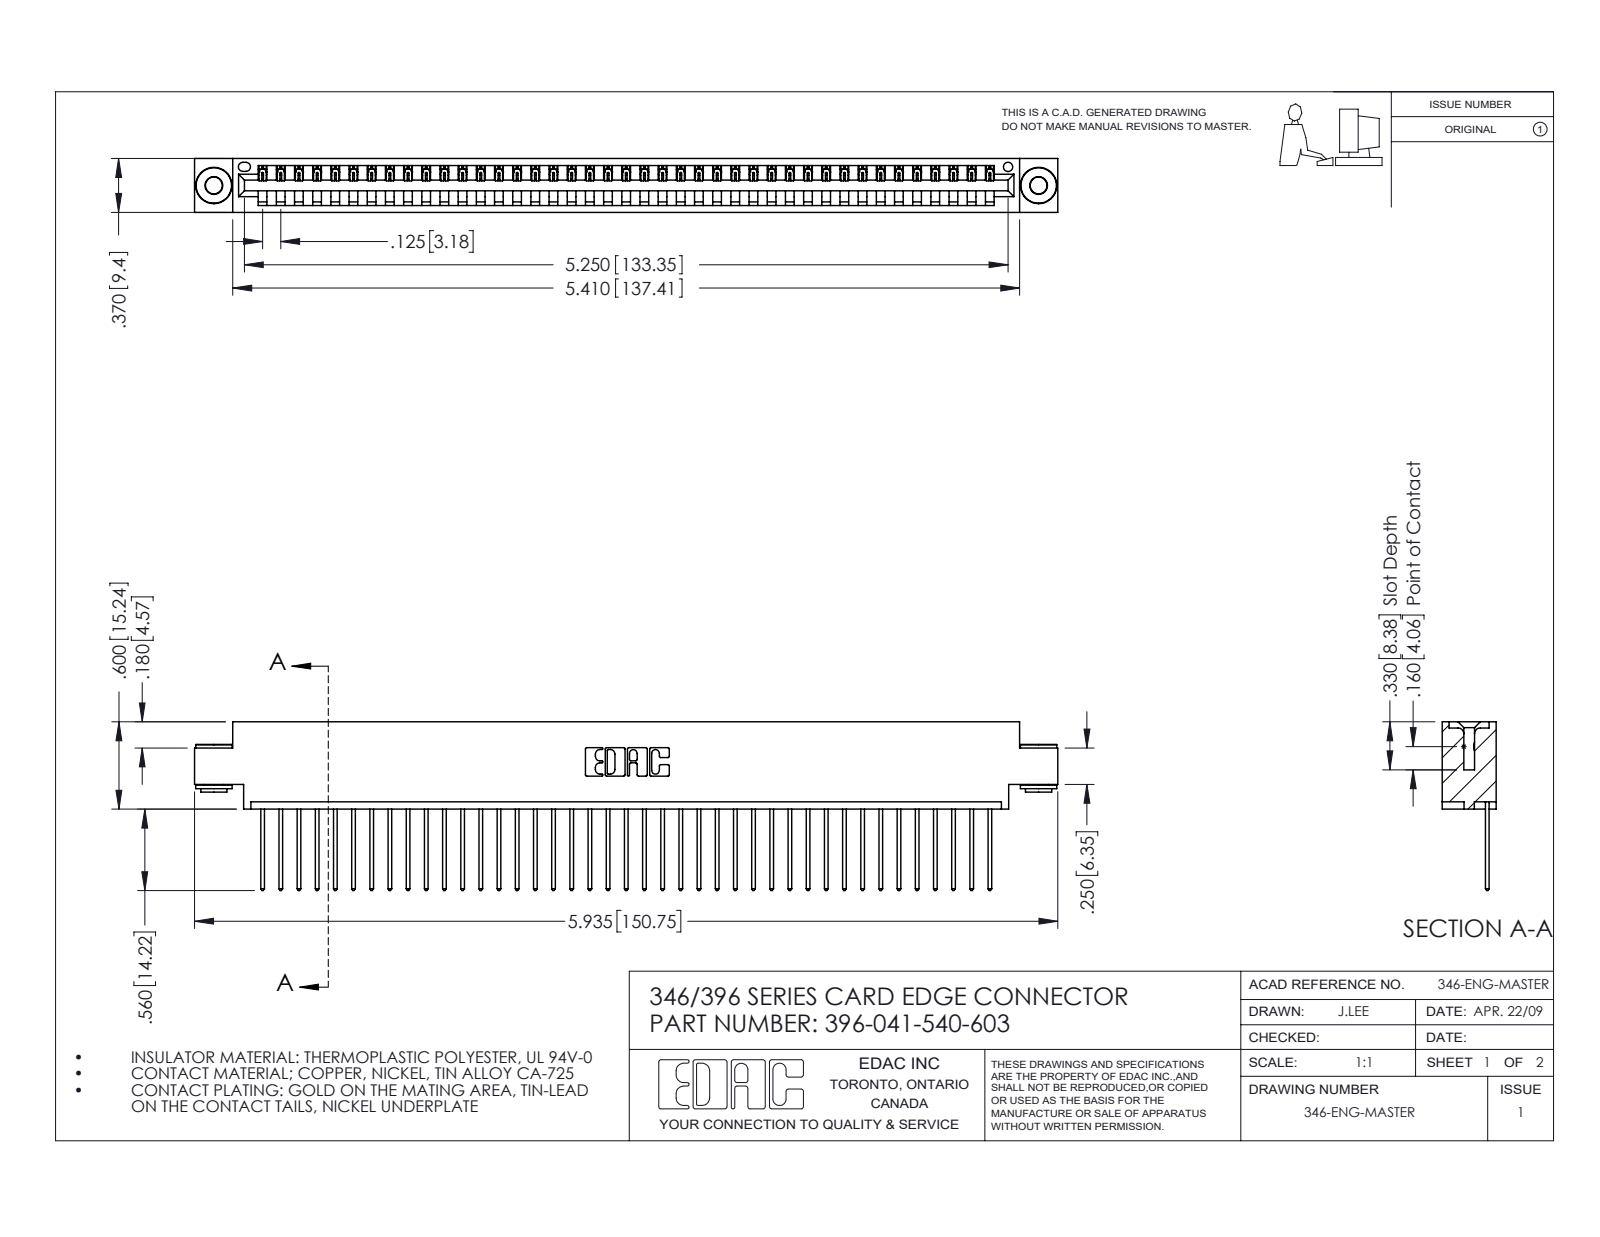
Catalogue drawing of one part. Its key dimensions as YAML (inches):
part_name: "345-250-002_345-250-002-102; 345-292-001_345-293-140; 346 Part_0.170 Offset - 0.156 Dia-TH; 396-041-540-603"
step_written_by: "SolidWorks 2016 (CONFIG_CONTROL_DESIGN)"
units: inches
bodies: {solids: 44, faces: 2542, planar: 1730, cylindrical: 804, other: 8}
overall_size: [5.935, 1.16, 0.37]
volume: 0.875
surface_area: 28.99
round_holes:
  - {diameter: 0.116, count: 2}
  - {diameter: 0.156, count: 2}
  - {diameter: 0.064, count: 1}
round_bosses_or_shafts:
  - {diameter: 0.25, count: 2}
  - {diameter: 0.18, count: 2}
  - {diameter: 0.136, count: 2}
partial_cylinders:
  - {radius: 0.006, count: 82}
  - {radius: 0.01, count: 82}
  - {radius: 0.01, count: 22}
  - {radius: 0.007, count: 6}
  - {radius: 0.031, count: 6}
  - {radius: 0.026, count: 3}
  - {radius: 0.031, count: 2}
  - {radius: 0.04, count: 2}
face_to_face_distances: [0.048, 0.322, 0.37, 0.25, 0.025, 0.072, 0.298, 0.148, 0.222, 0.1]
hole_center_spacings: [0.246, 5.461, 5.67]
